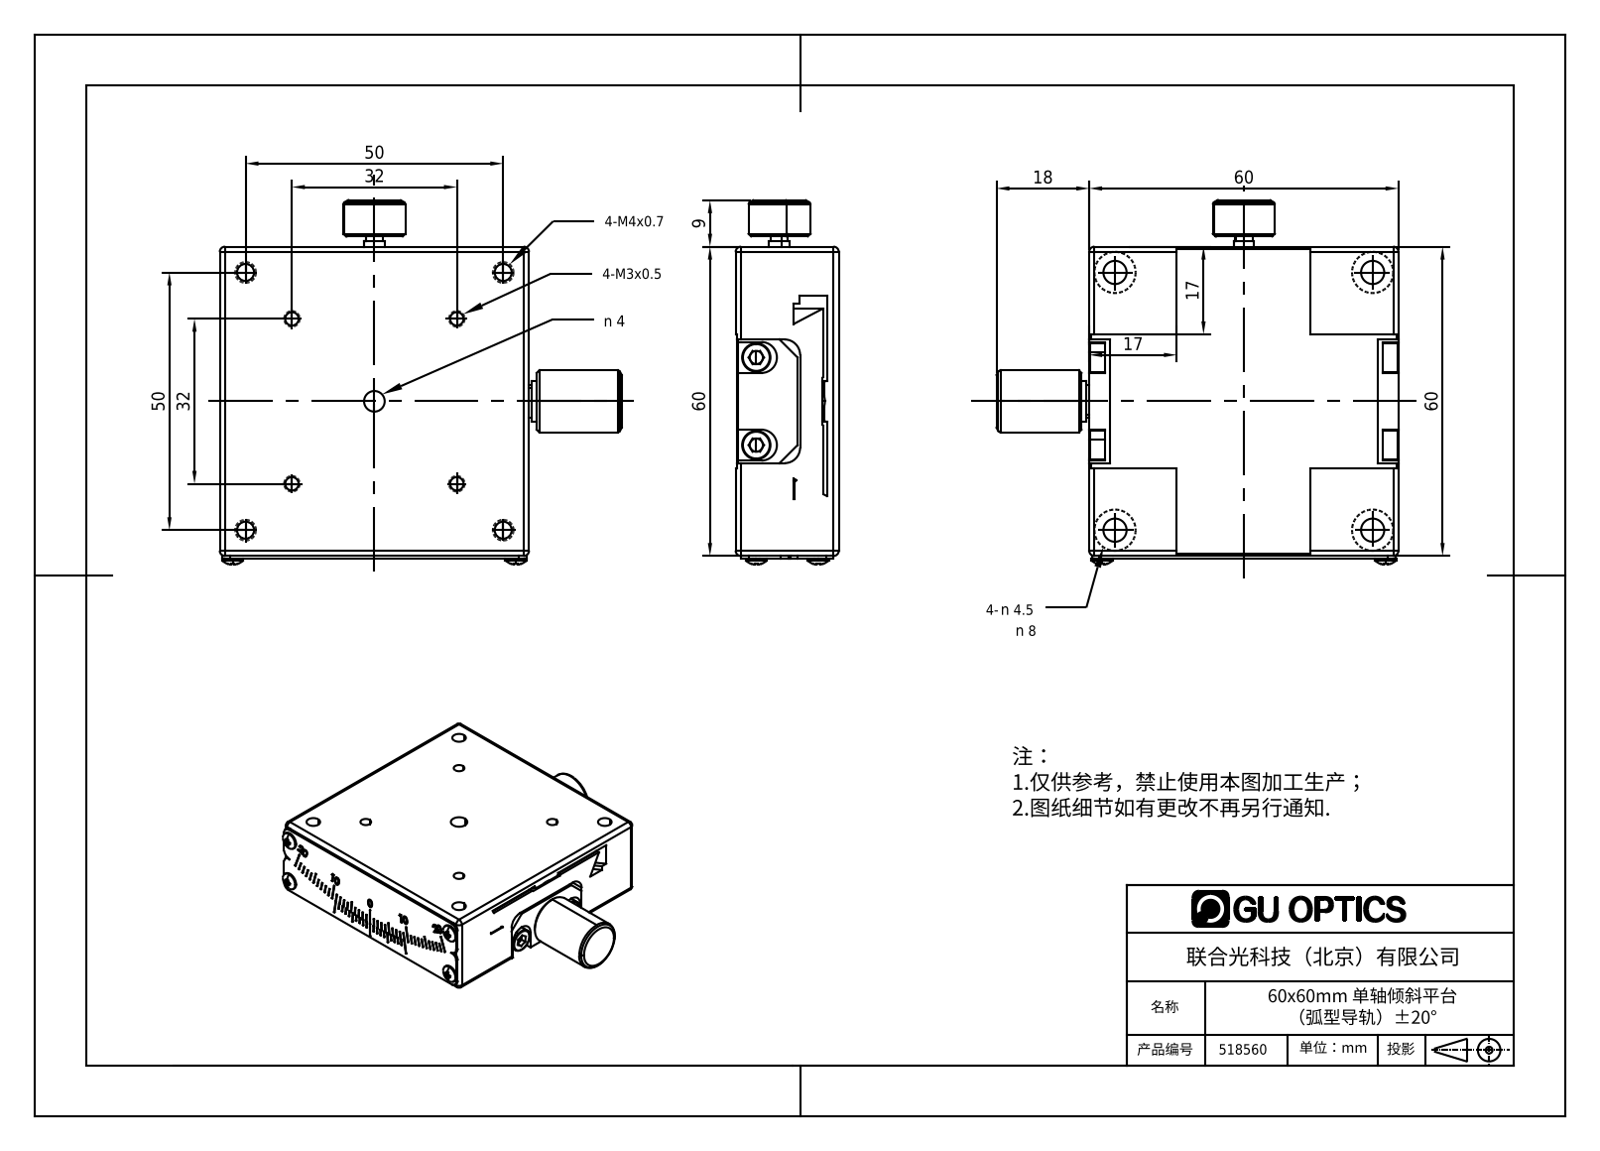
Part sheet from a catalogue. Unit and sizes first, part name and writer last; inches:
Units: inches
Overall size (bounding box): 3.071 × 2.781 × 0.787
Round holes (diameter × count): ⌀0.102 ×4, ⌀0.13 ×4, ⌀0.177 ×4, ⌀0.315 ×4, ⌀0.157 ×1
Round bosses / shafts (diameter × count): ⌀0.165 ×4, ⌀0.472 ×2, ⌀0.217 ×2, ⌀0.315 ×1, ⌀0.252 ×1, ⌀0.157 ×1, ⌀0.13 ×1
Partial cylindrical surfaces — rounded edges, fillets, slot ends (radius × count): R0.039 ×12, R0.059 ×8, R0.118 ×4, R0.133 ×1, R0.177 ×1, R2.717 ×1, R2.736 ×1, R2.742 ×1
Main face-to-face distances: 0.78, 0.787, 2.382, 2.362, 0.295, 0.02, 0.374, 0.472, 2.008, 0.276
Hole centre spacings: 1.653, 0.501, 0.891, 1.26, 1.392, 1.969, 2.283, 1.781
Volume: 4.278 in³ · Surface area: 34.01 in²
Bodies: 1 solid, 898 faces (525 planar, 176 cylindrical, 197 other)
Part name (STEP PRODUCT): MXG6-60CS
STEP written by: SolidWorks 2020 (CONFIG_CONTROL_DESIGN)
